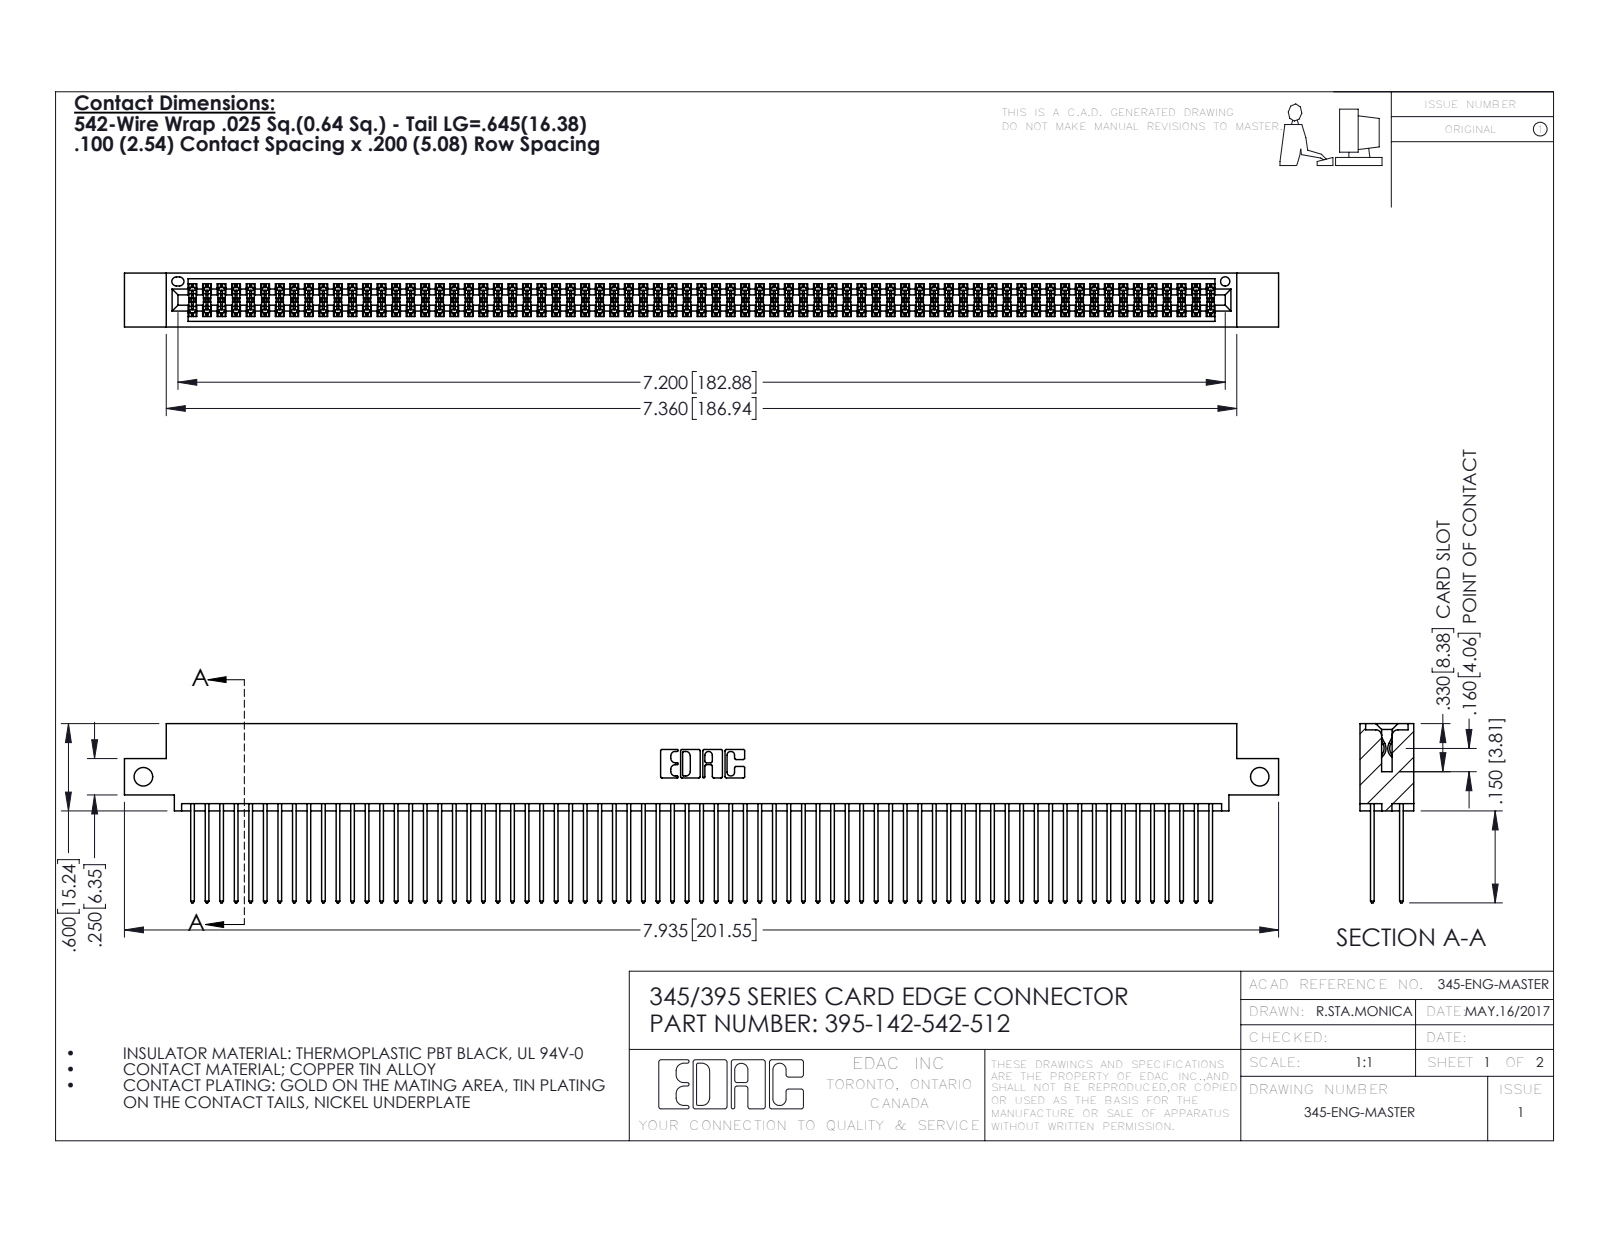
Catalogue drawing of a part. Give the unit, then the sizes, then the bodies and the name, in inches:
Units: inches
Overall size (bounding box): 7.935 × 1.232 × 0.37
Round holes (diameter × count): ⌀0.128 ×2, ⌀0.064 ×1
Partial cylindrical surfaces — rounded edges, fillets, slot ends (radius × count): R0.006 ×213, R0.01 ×142, R0.01 ×22, R0.007 ×6, R0.031 ×6, R0.026 ×3, R0.014 ×2, R0.019 ×2
Main face-to-face distances: 0.298, 0.072, 0.2, 0.098, 0.272, 0.025, 0.225, 0.37, 0.175, 0.149
Hole centre spacings: 7.675
Volume: 1.242 in³ · Surface area: 52.22 in²
Bodies: 143 solids, 7230 faces (4770 planar, 2460 cylindrical, 0 other)
Part name (STEP PRODUCT): 345-292-001_345-293-142; 395-142-542-512; 345 Part_0.110 Offset - Side Mount
STEP written by: SolidWorks 2016 (CONFIG_CONTROL_DESIGN)
